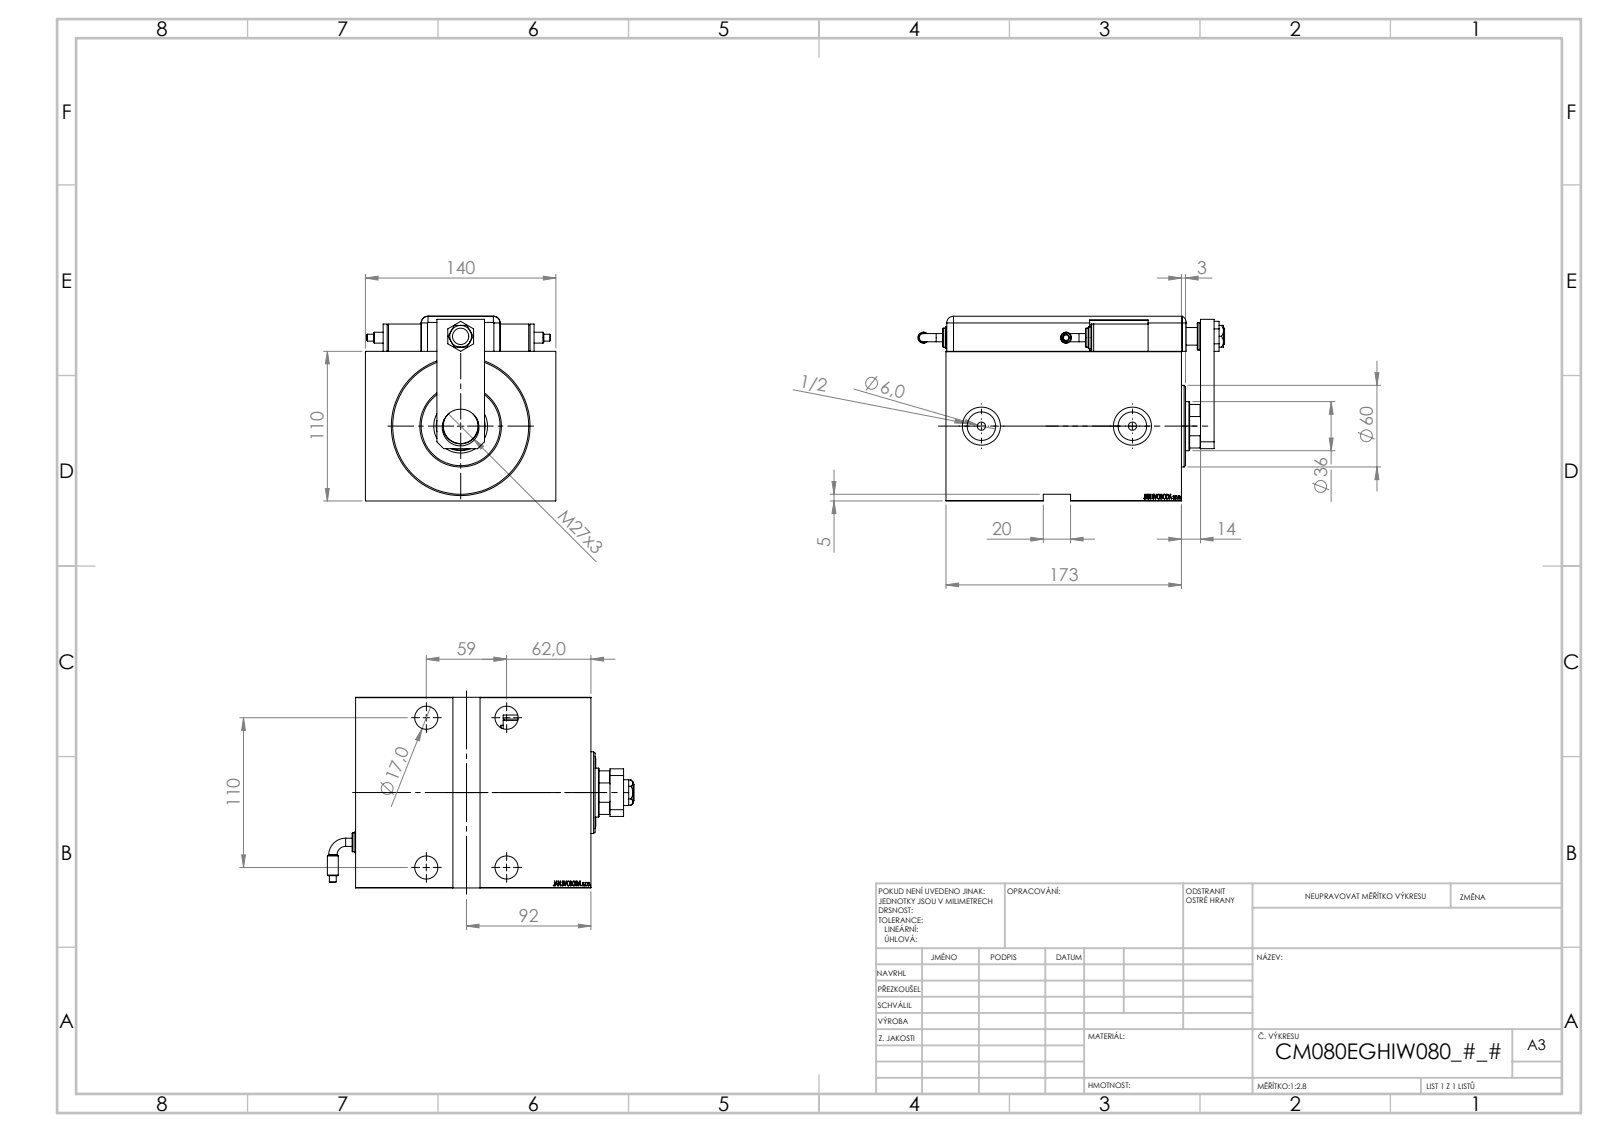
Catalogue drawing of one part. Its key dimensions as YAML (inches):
part_name: "SWITCH_Q_FRONT_BACK; SWITCH DIM A_G; TYC; MAGNETIC SWITCH Q (+7 more)"
step_written_by: "SolidWorks 2019 (CONFIG_CONTROL_DESIGN)"
units: inches
bodies: {solids: 13, faces: 1271, planar: 621, cylindrical: 117, other: 533}
overall_size: [8.876, 5.512, 5.346]
volume: 139.9
surface_area: 491.6
round_holes:
  - {diameter: 0.669, count: 4}
  - {diameter: 0.984, count: 4}
  - {diameter: 0.157, count: 2}
  - {diameter: 0.236, count: 2}
  - {diameter: 0.315, count: 2}
  - {diameter: 0.825, count: 2}
  - {diameter: 1.102, count: 2}
  - {diameter: 0.472, count: 1}
  - {diameter: 0.512, count: 1}
  - {diameter: 0.551, count: 1}
  - {diameter: 1.004, count: 1}
  - {diameter: 1.063, count: 1}
round_bosses_or_shafts:
  - {diameter: 0.787, count: 3}
  - {diameter: 0.63, count: 2}
  - {diameter: 0.551, count: 2}
  - {diameter: 0.315, count: 2}
  - {diameter: 0.236, count: 2}
  - {diameter: 0.198, count: 2}
  - {diameter: 2.362, count: 1}
partial_cylinders:
  - {radius: 0.197, count: 9}
  - {radius: 0.394, count: 1}
  - {radius: 0.689, count: 1}
face_to_face_distances: [4.331, 5.512, 0.118, 6.811, 0.827, 5.984, 5.346, 1.016, 0.197, 0.898]
hole_center_spacings: [2.323, 2.798, 3.352, 4.331, 4.825, 4.914, 5.167, 0.039]
